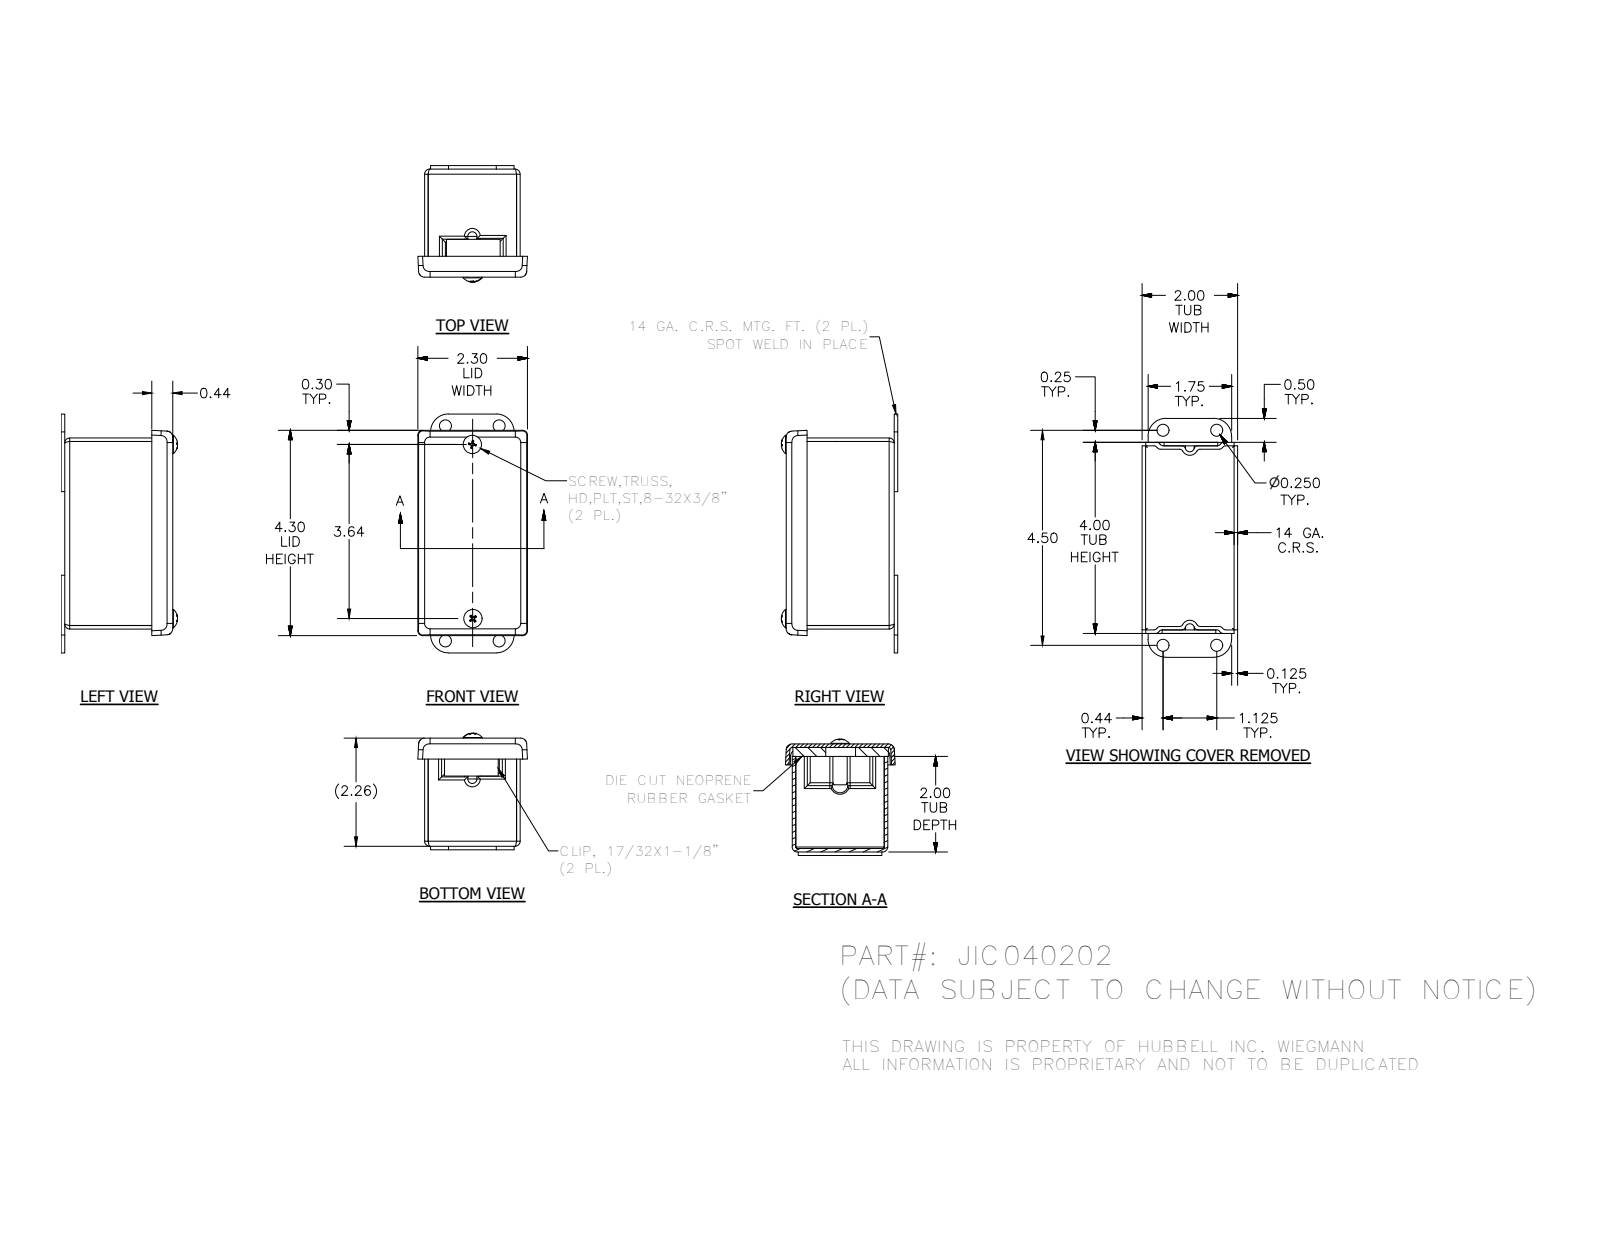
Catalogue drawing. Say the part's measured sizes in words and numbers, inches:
The part is named "BR4X2P; 316271; JIC422P; 31811 (+3 more)". Its 3-D file was written by "Autodesk Inventor 2014 (AUTOMOTIVE_DESIGN)". It is 9 solids with 315 faces: 117 planar, 92 cylindrical and 106 other. Overall it measures 5.007 by 2.445 by 2.328 inches. Its volume is 4.919 cubic inches and its surface area 122.2 square inches. Round holes: 4 of diameter 0.25, 2 of diameter 0.219. Round bosses or shafts: 2 of diameter 0.384, 2 of diameter 0.164. Partial cylindrical surfaces (rounded edges, fillets, slot ends): 38 of radius 0.071, 8 of radius 0.125, 6 of radius 0.1, 4 of radius 0.026, 4 of radius 0.031, 4 of radius 0.051, 4 of radius 0.094, 4 of radius 0.105. The main face-to-face distances are 0.074, 1.926, 2.187, 2, 2.261, 1.852, 0.261, 0.187, 2.113, 3.926. The hole center spacings are 4.116, 4.5, 4.639, 0.683, 0.683, 0.704, 0.704, 1.125.
